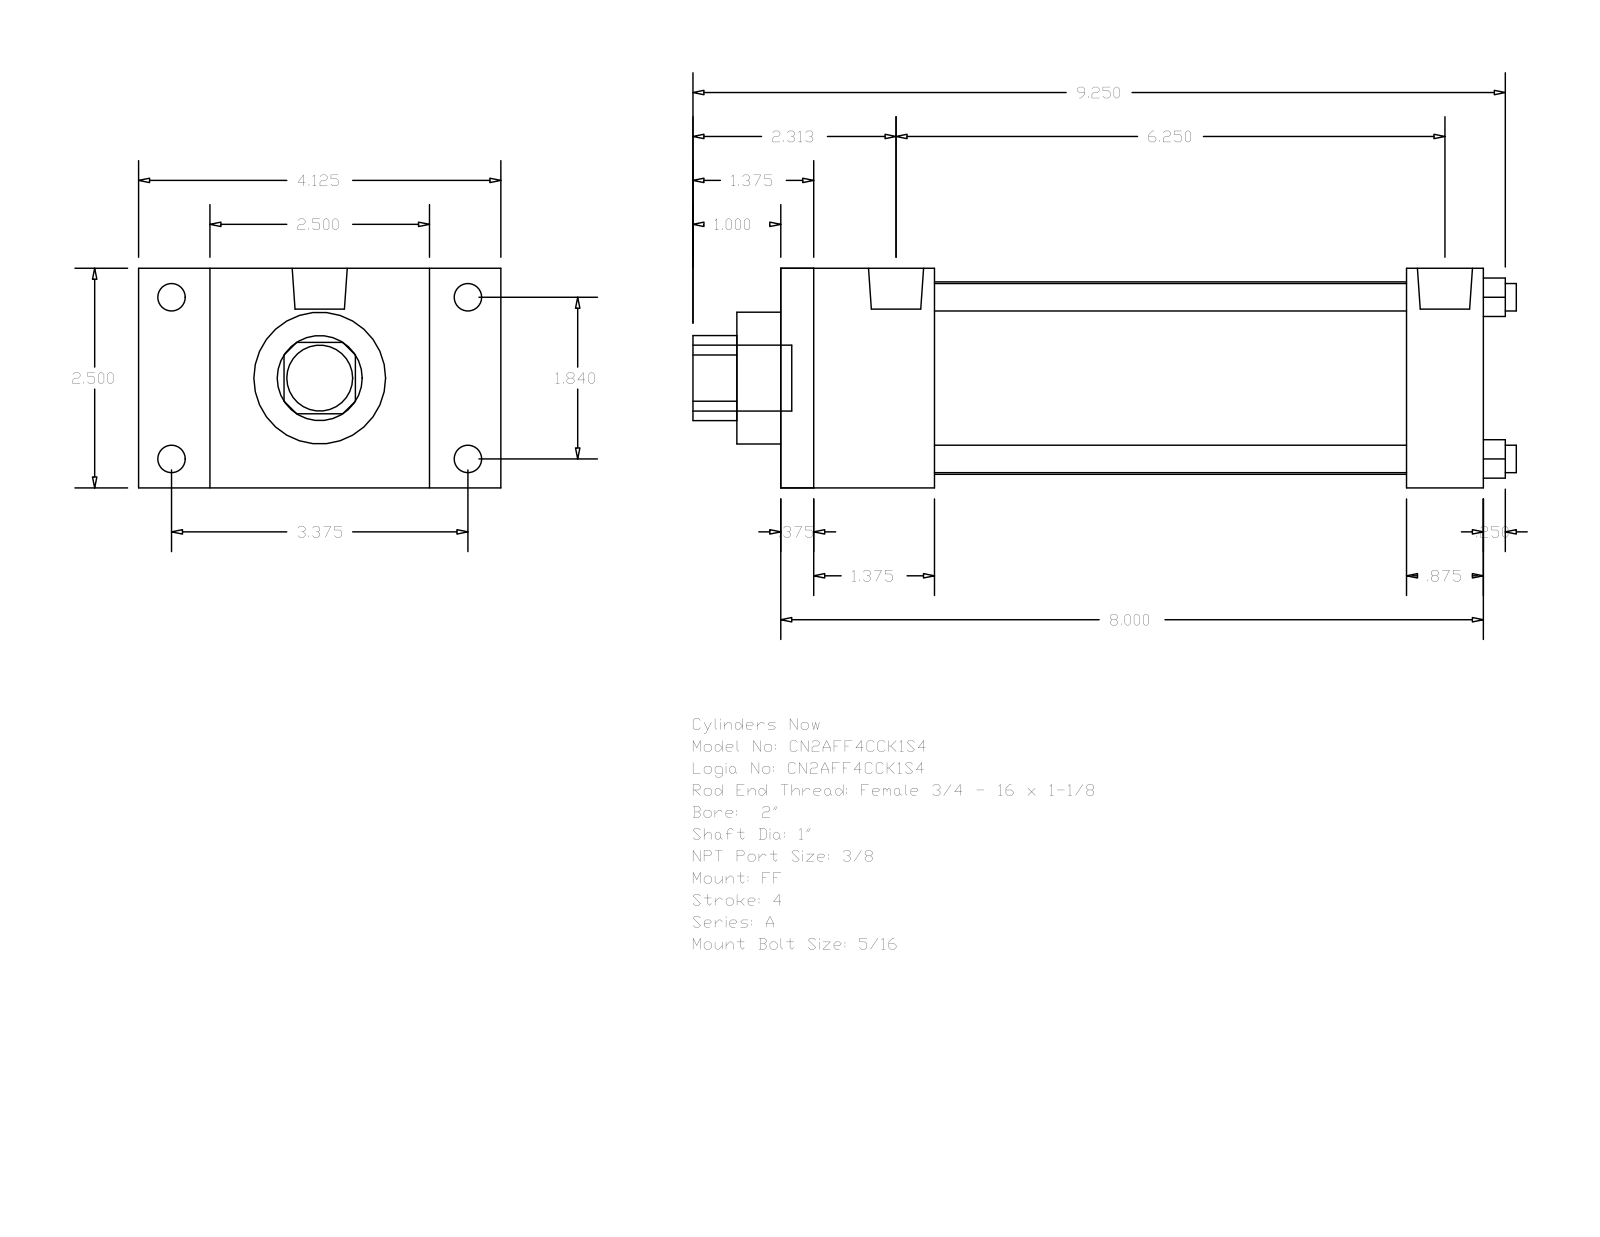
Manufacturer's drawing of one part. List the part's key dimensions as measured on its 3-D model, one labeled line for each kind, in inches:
Part name (STEP PRODUCT): A_FF__0200_1
STEP written by: GSSL Pune (CONFIG_CONTROL_DESIGN)
Units: inches
Bodies: 0 solids, 92 faces (64 planar, 28 cylindrical, 0 other)
Overall size (bounding box): 9.375 × 4.125 × 2.5
Round holes (diameter × count): ⌀0.313 ×4, ⌀1 ×1, ⌀1.5 ×1, ⌀2.19 ×1
Round bosses / shafts (diameter × count): ⌀0.313 ×4, ⌀0.219 ×4, ⌀0.627 ×2, ⌀0.75 ×1
Partial cylindrical surfaces — rounded edges, fillets, slot ends (radius × count): R0.484 ×1
Main face-to-face distances: 2.5, 8, 7.625, 0.375, 0.875, 0.813, 1.75, 7.125, 1.375, 6.75
Hole centre spacings: 1.301, 1.84, 2.602
